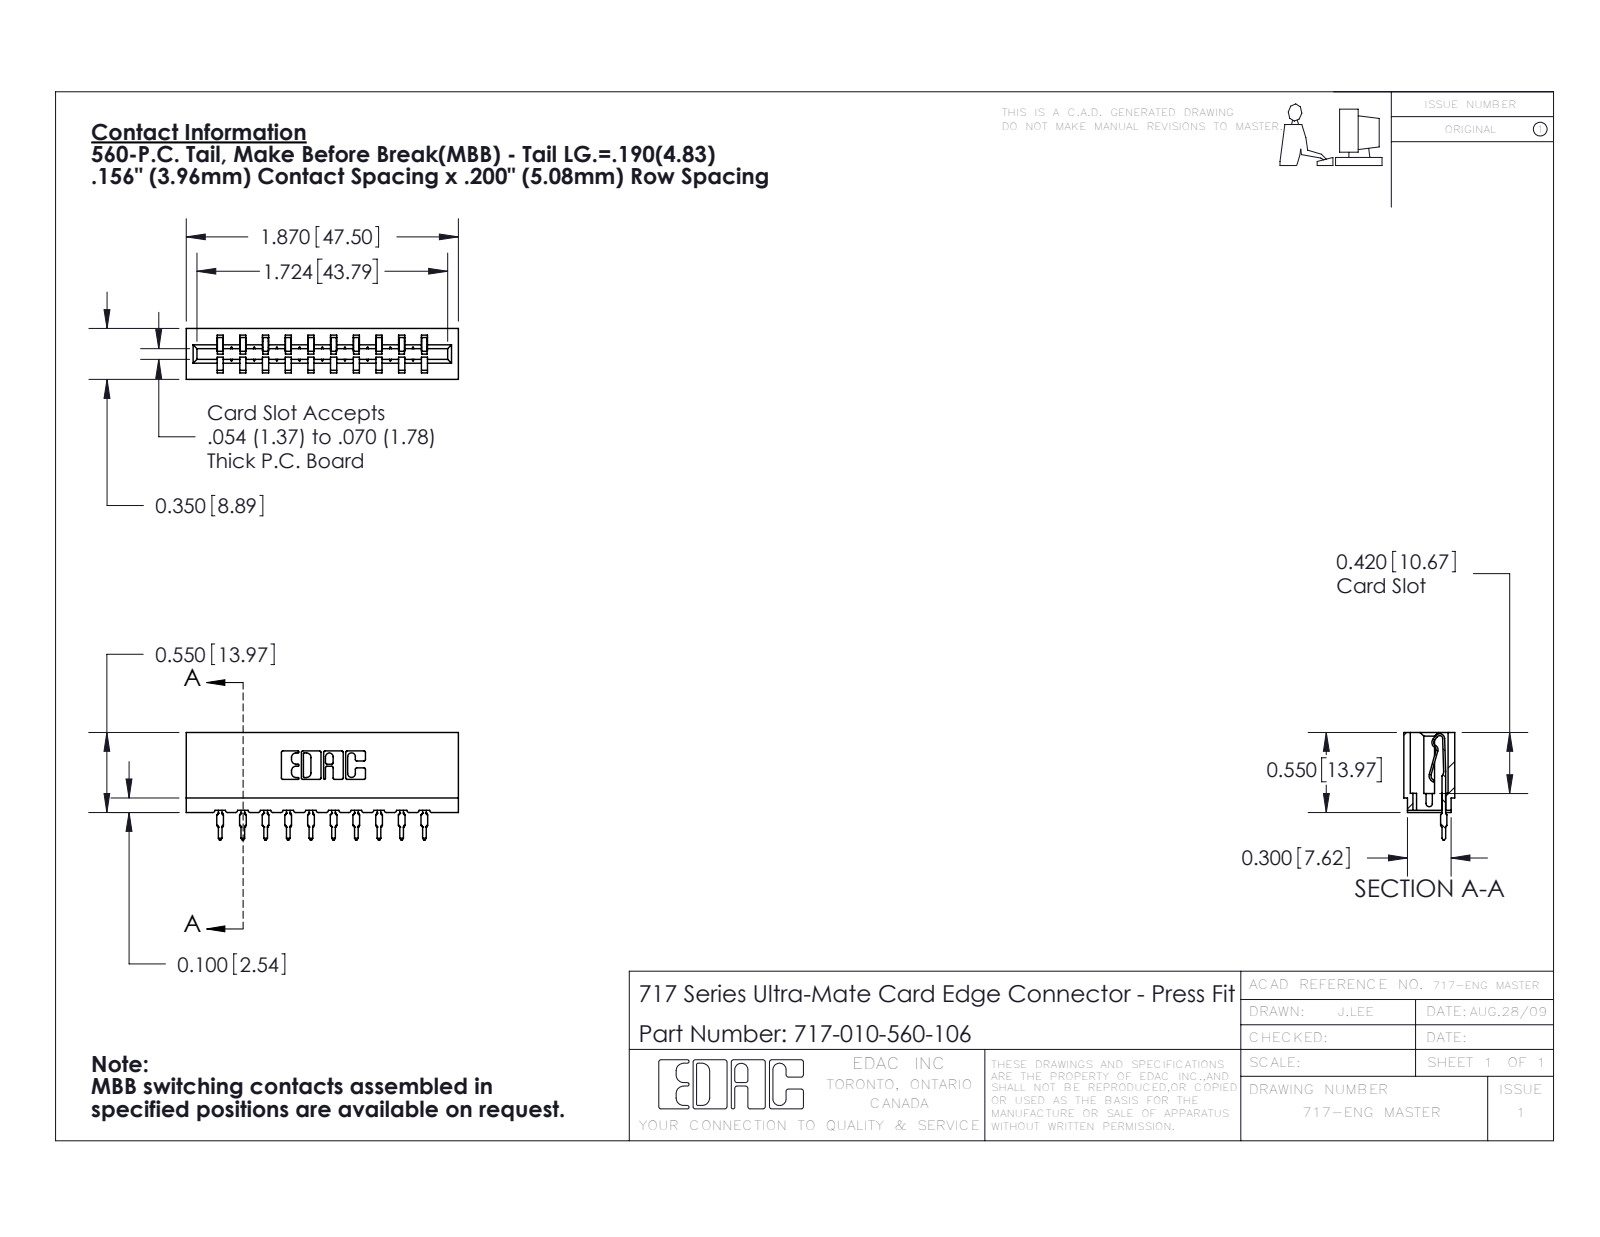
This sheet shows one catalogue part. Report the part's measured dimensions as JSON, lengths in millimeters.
{"part_name": "717 Part_Insulator Option - 06; 717-010-560-106; 745-292-001_560", "step_written_by": "SolidWorks 2016 (CONFIG_CONTROL_DESIGN)", "units": "millimeters", "bodies": {"solids": 11, "faces": 1314, "planar": 784, "cylindrical": 270, "other": 260}, "overall_size": [47.5, 18.8, 8.9], "volume_mm3": 4200, "surface_area_mm2": 5695, "partial_cylinders_radius": [[0.3, 22], [0.4, 20], [0.5, 20], [0.2, 6], [0.8, 6], [0.1, 4], [0.3, 4], [0.7, 3]], "face_to_face_distances": [4, 5.4, 3.5, 15.8, 8.9, 5, 11.9, 7.9, 9, 7.9]}
